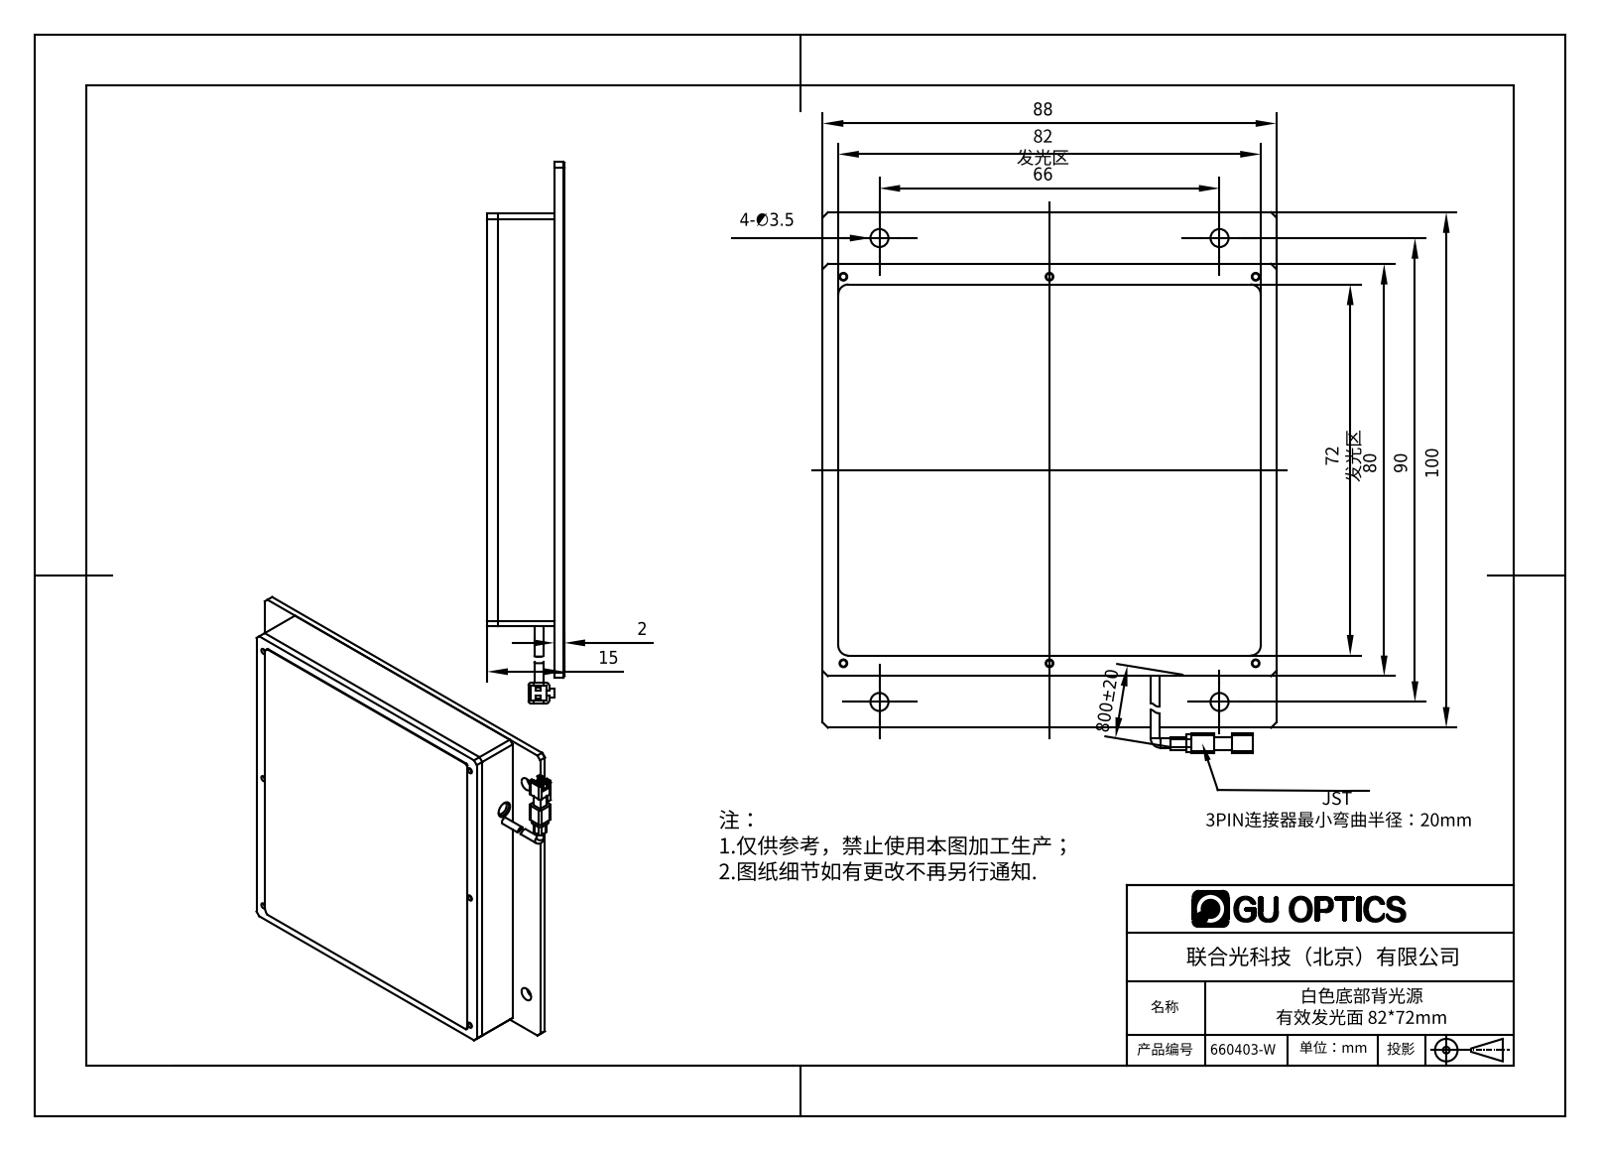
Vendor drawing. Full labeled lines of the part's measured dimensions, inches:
Part name (STEP PRODUCT): 660403-W
STEP written by: SolidWorks 2016 (AUTOMOTIVE_DESIGN)
Units: inches
Bodies: 5 solids, 421 faces (188 planar, 134 cylindrical, 99 other)
Overall size (bounding box): 4.134 × 3.465 × 0.598
Volume: 2.729 in³ · Surface area: 66.97 in²
Round holes (diameter × count): ⌀0.049 ×12, ⌀0.063 ×12, ⌀0.059 ×6, ⌀0.094 ×6, ⌀0.11 ×6, ⌀0.138 ×4, ⌀0.142 ×1
Round bosses / shafts (diameter × count): ⌀0.069 ×2
Partial cylindrical surfaces — rounded edges, fillets, slot ends (radius × count): R0.02 ×8, R0.039 ×8, R0.079 ×4, R0.059 ×2, R0.026 ×1, R0.026 ×1, R0.067 ×1, R0.078 ×1
Main face-to-face distances: 0.079, 0.512, 0.433, 0.087, 0.598, 0.52, 0.118, 0.157, 2.992, 3.346
Hole centre spacings: 1.575, 3.15, 3.364, 0.02, 2.972, 0.39, 0.404, 1.328
